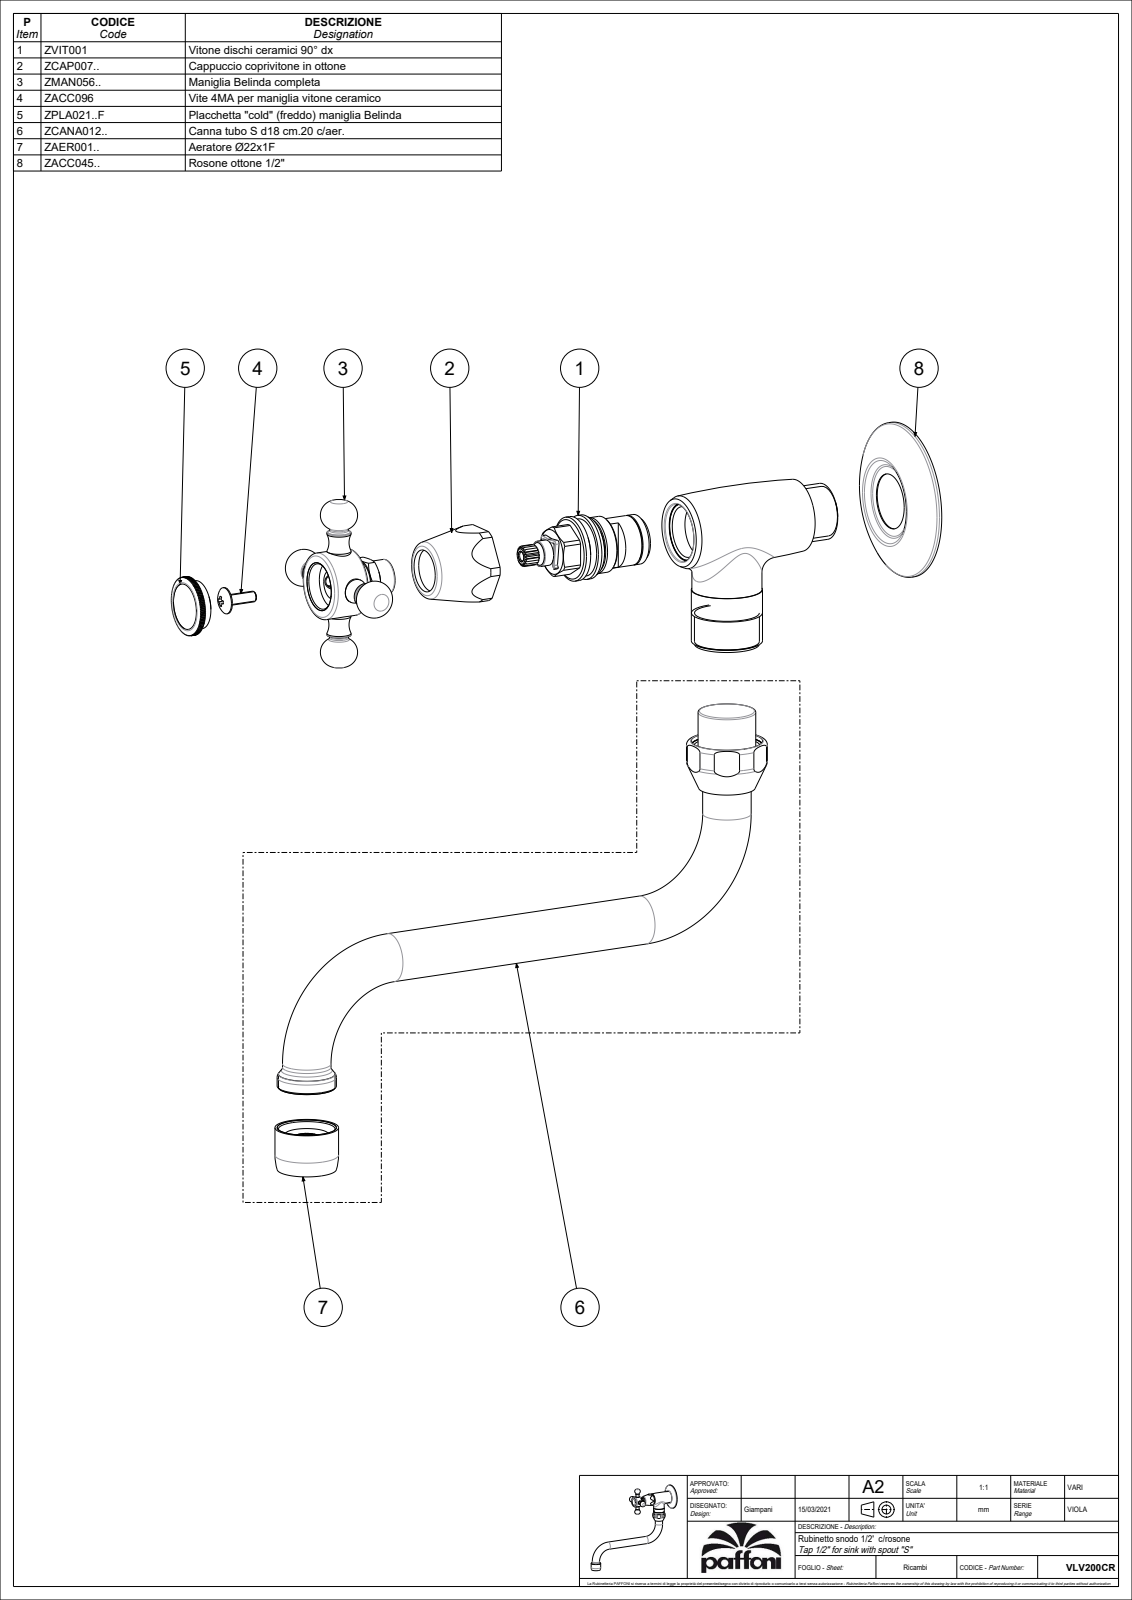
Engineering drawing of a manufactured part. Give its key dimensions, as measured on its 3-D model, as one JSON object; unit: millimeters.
{"part_name": "VLV200CR", "step_written_by": "CREO PARAMETRIC BY PTC INC, 2020044 (CONFIG_CONTROL_DESIGN)", "units": "millimeters", "bodies": {"solids": 1, "faces": 511, "planar": 237, "cylindrical": 162, "other": 112}, "overall_size": [233.8, 190.44, 64.07], "volume_mm3": 167128, "surface_area_mm2": 36238, "round_bosses_or_shafts": [[18, 3], [9, 2], [7, 2], [58, 1], [26.4, 1], [26, 1], [25, 1], [23.6, 1]], "partial_cylinders_radius": [[11, 1], [14.5, 1], [15, 1]], "face_to_face_distances": [91, 26.5, 6.7, 97.7, 86.5, 20.75, 5.75, 28.49, 79.8, 11.2]}
